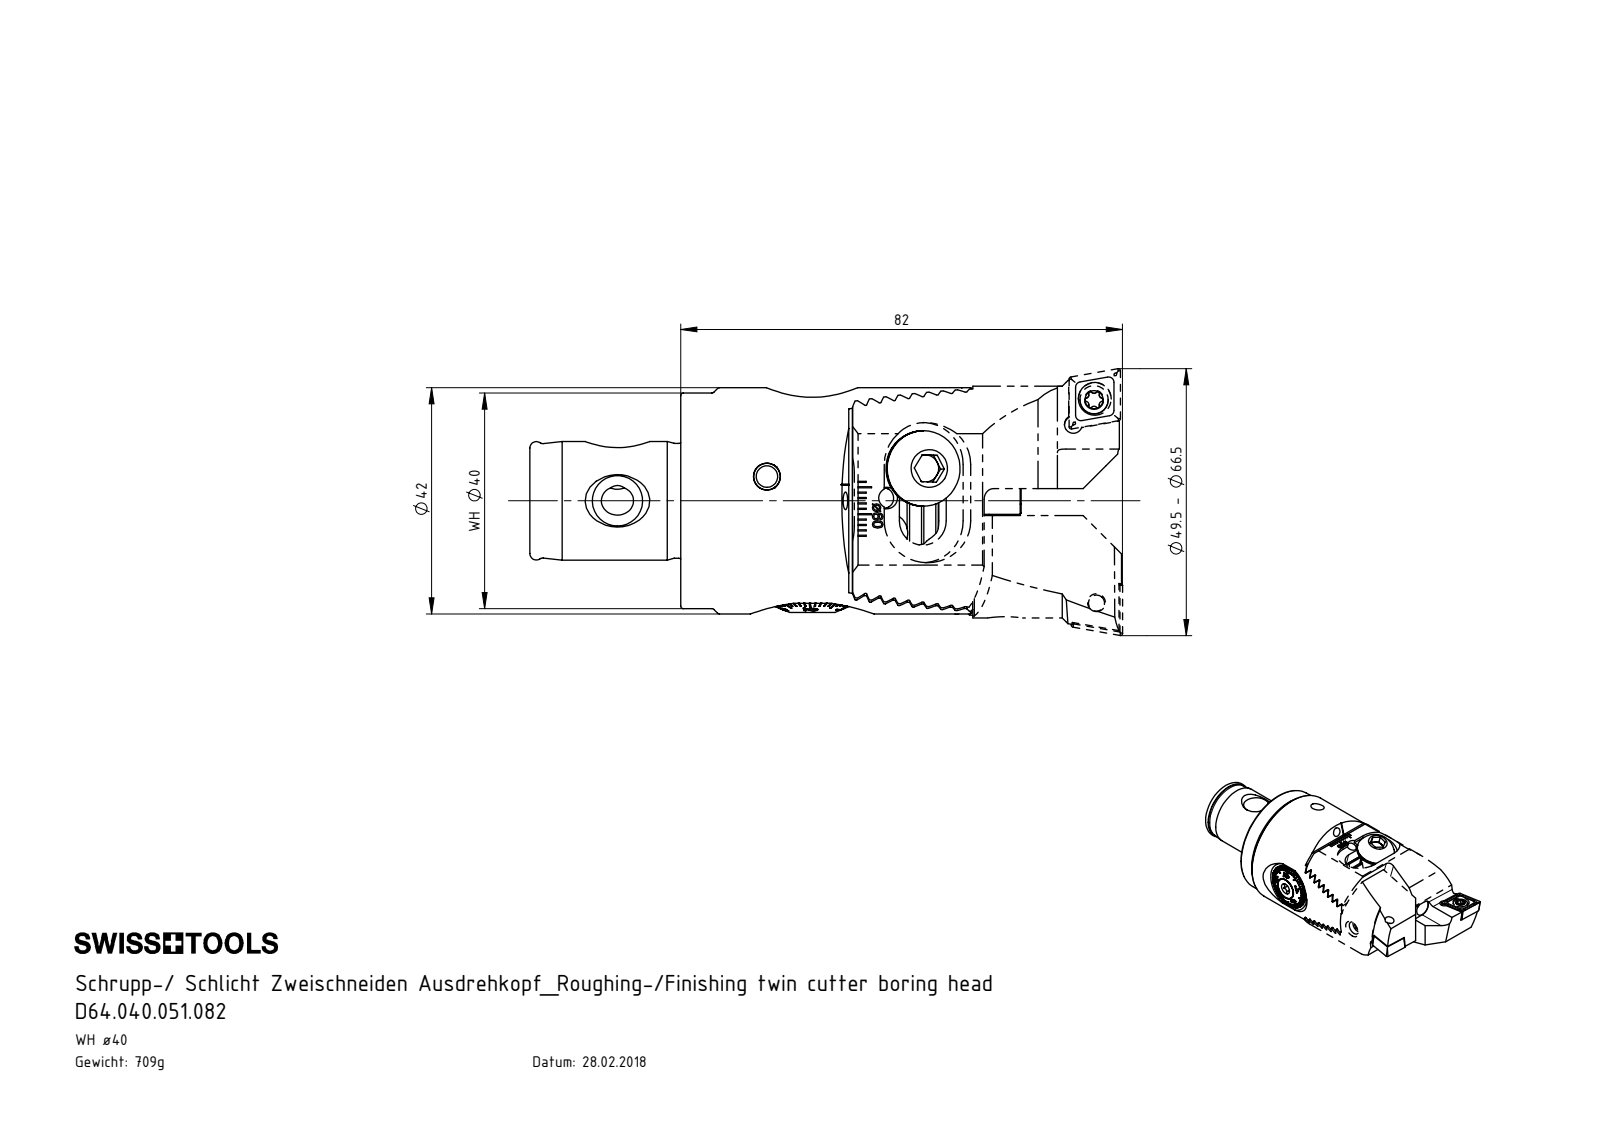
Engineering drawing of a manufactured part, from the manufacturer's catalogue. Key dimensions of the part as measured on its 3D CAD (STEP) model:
Part name (STEP PRODUCT): WH4-ZC4.K23.082_A; ZC4-xxx.001.028_A_versetzt mit FV; WCB-ER2.001.009_A; CCMT09T304 (+8 more)
STEP written by: SolidWorks 2017 (CONFIG_CONTROL_DESIGN)
Units: millimetres
Bodies: 23 solids, 1479 faces (741 planar, 278 cylindrical, 460 other)
Overall size (bounding box): 110 × 49.5 × 42
Volume: 90 721 mm³ · Surface area: 38 034 mm²
Round holes (diameter × count): ⌀3.3 ×8, ⌀5 ×3, ⌀6.8 ×3, ⌀3 ×2, ⌀4.4 ×2, ⌀6.1 ×2, ⌀8.4 ×2, ⌀9 ×2, ⌀1.6 ×1, ⌀2 ×1, ⌀2.5 ×1, ⌀2.9 ×1
Round bosses / shafts (diameter × count): ⌀4 ×5, ⌀14 ×4, ⌀8 ×3, ⌀5.25 ×2, ⌀42 ×1, ⌀40 ×1, ⌀22 ×1, ⌀21.3 ×1
Partial cylindrical surfaces — rounded edges, fillets, slot ends (radius × count): R0.2 ×18, R0.2 ×16, R0.34 ×12, R0.59 ×12, R2 ×5, R1.6 ×4, R4.5 ×4, R7.75 ×4
Main face-to-face distances: 2.38, 4.76, 7.14, 2.34, 2.42, 4.8, 9.52, 4.72, 11.9, 11.91
Hole centre spacings: 6.19, 33.71, 5.99, 6.07, 6.5, 6.73, 12, 28.78
